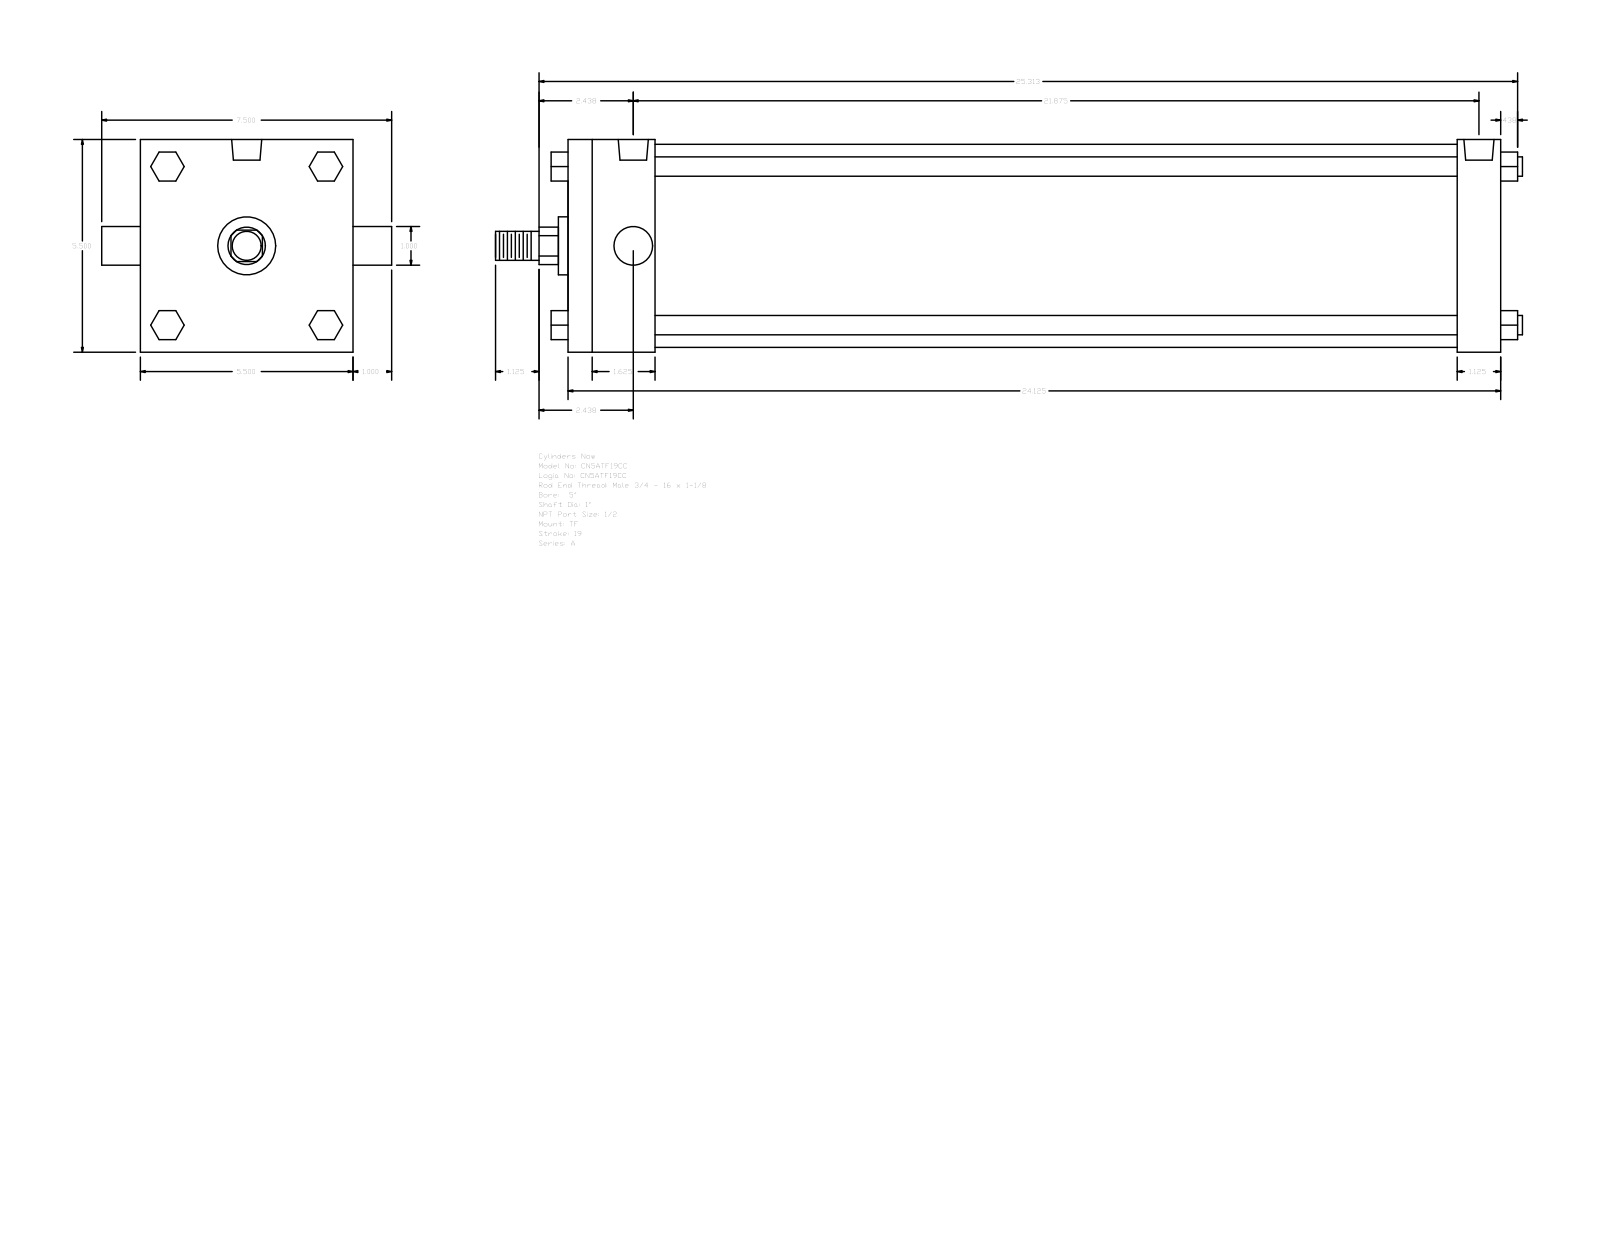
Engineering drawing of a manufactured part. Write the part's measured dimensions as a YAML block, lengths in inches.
part_name: "A_TF__0500_1"
step_written_by: "GSSL Pune (CONFIG_CONTROL_DESIGN)"
units: inches
bodies: {solids: 0, faces: 120, planar: 92, cylindrical: 28, other: 0}
overall_size: [26.563, 7.5, 5.5]
round_holes:
  - {diameter: 0.344, count: 3}
  - {diameter: 0.778, count: 2}
round_bosses_or_shafts:
  - {diameter: 0.5, count: 4}
  - {diameter: 1, count: 2}
  - {diameter: 5.25, count: 1}
  - {diameter: 1.5, count: 1}
  - {diameter: 0.75, count: 1}
partial_cylinders:
  - {radius: 0.484, count: 1}
face_to_face_distances: [5.5, 24.125, 23, 1.125, 2.25, 20.75, 21.875, 0.75, 2.05, 3.55]
hole_center_spacings: [0.094, 21.781, 21.687, 21.875]
